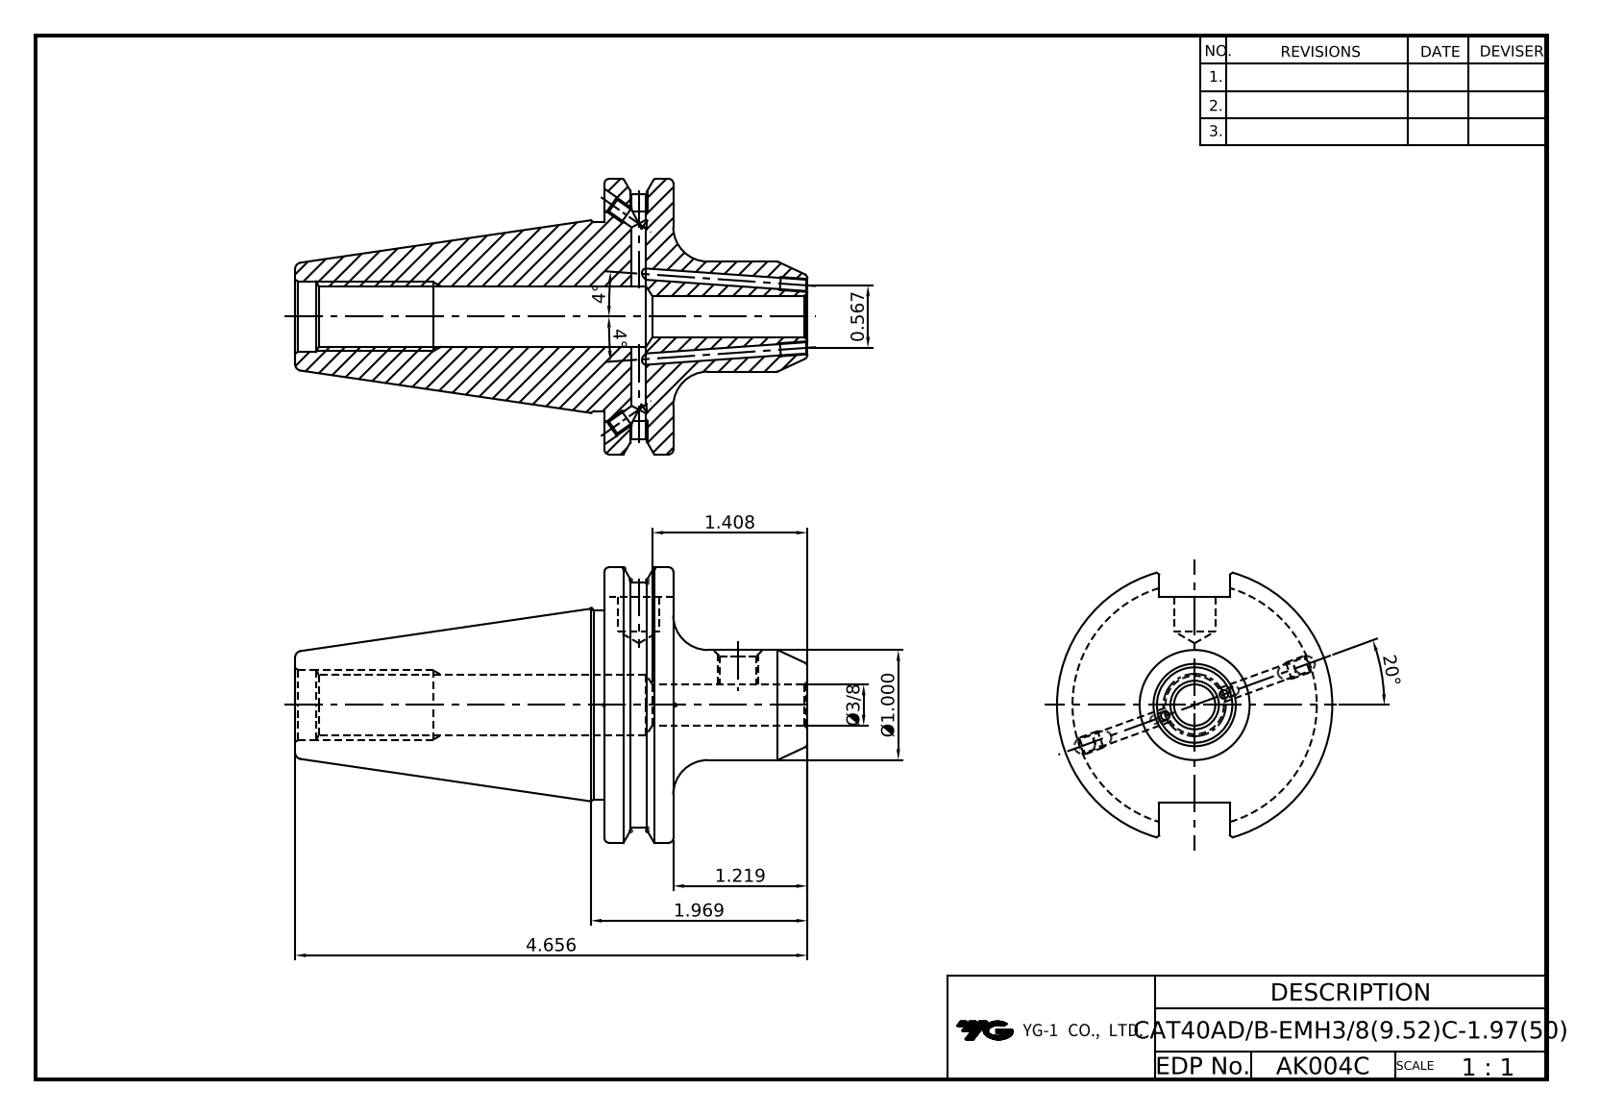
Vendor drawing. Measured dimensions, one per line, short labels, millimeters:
name: LO-CAT40ADB-EMH9.525C-50
written by: Autodesk Inventor 2022 (AUTOMOTIVE_DESIGN)
unit: mm
bodies: 1 solid, 89 faces (36 planar, 30 cylindrical, 23 other)
size: 118.25 × 63.5 × 61.09
volume: 113 625 mm³; area: 24 482 mm²
holes: 4× ⌀3.24, 2× ⌀2.6, 2× ⌀4, 2× ⌀4.2, 2× ⌀9.53, 1× ⌀8.38, 1× ⌀13, 1× ⌀13.39, 1× ⌀16.3
bosses: 1× ⌀63.5, 1× ⌀43.6, 1× ⌀25.4
rounds: 1× R28.15
face distances: 15.88, 47.6, 46.83, 30.95, 16.38, 71.42, 87.3, 118.25, 77.47, 6.05
hole spacings: 22.87
